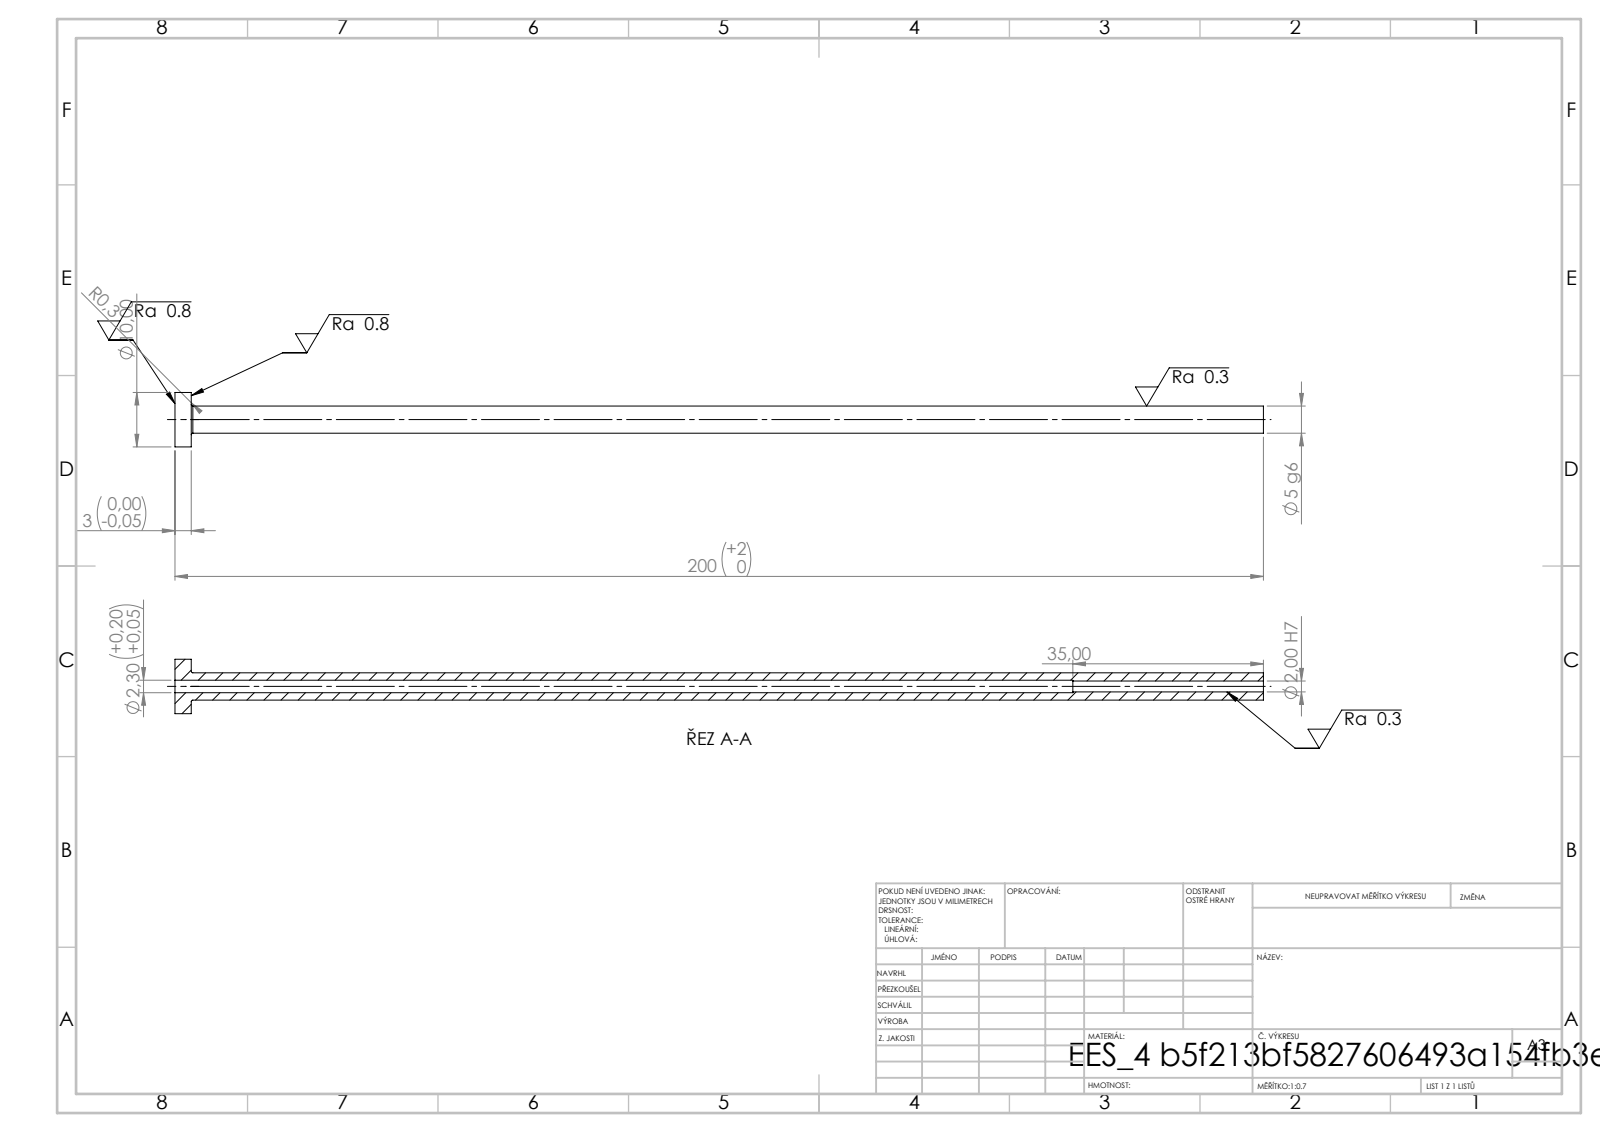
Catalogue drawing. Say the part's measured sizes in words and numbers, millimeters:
Its 3-D file was written by "SolidWorks 2019 (CONFIG_CONTROL_DESIGN)". It is 1 solid with 14 faces: 4 planar, 8 cylindrical and 2 other. Overall it measures 200 by 10 by 10 millimeters. Its volume is 3 309 cubic millimeters and its surface area 4 750 square millimeters. Round holes: 1 of diameter 2, 1 of diameter 2.3. Round bosses or shafts: 1 of diameter 10, 1 of diameter 5. The main face-to-face distances are 3, 200, 197, 165, 162, 35.
